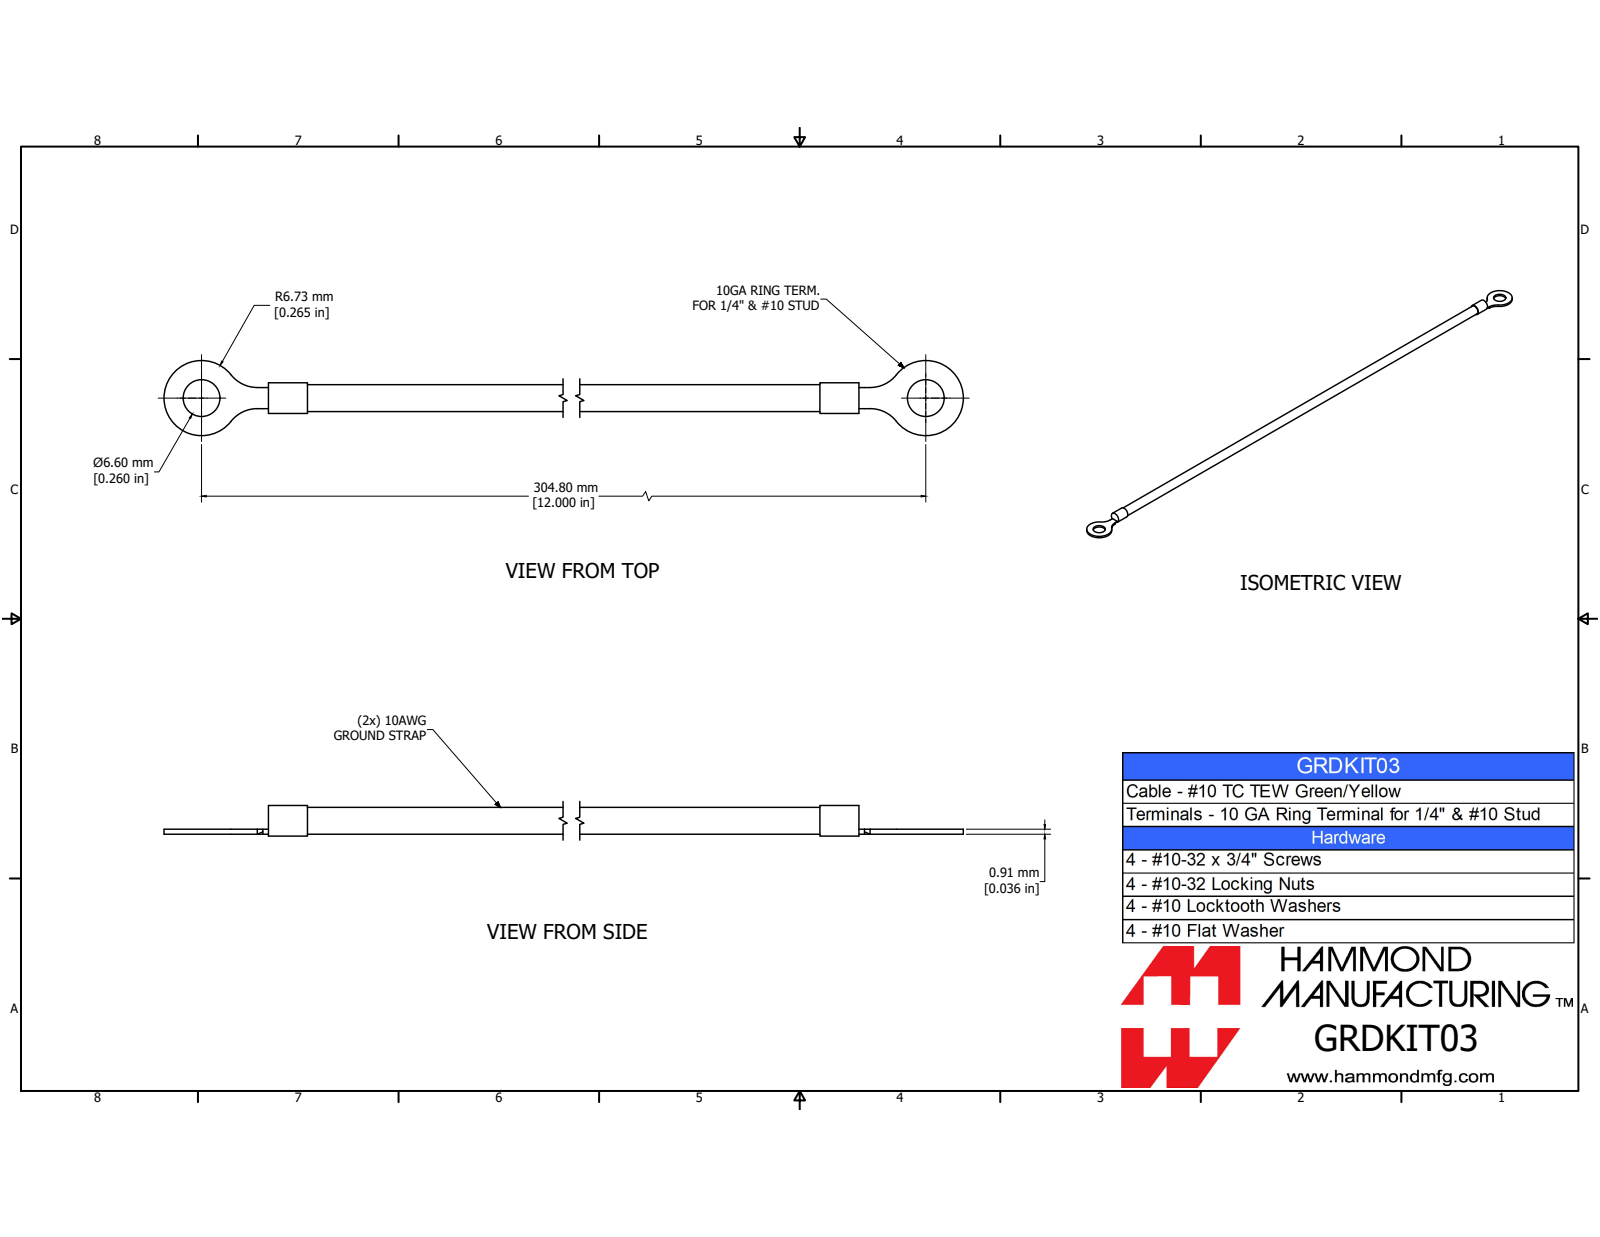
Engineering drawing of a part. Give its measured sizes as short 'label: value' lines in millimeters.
name: GRDKIT03
written by: Autodesk Inventor 2015 (AUTOMOTIVE_DESIGN)
unit: mm
bodies: 1 solid, 27 faces (8 planar, 13 cylindrical, 6 other)
size: 318.26 × 13.46 × 5.5
volume: 5 450 mm³; area: 4 990 mm²
holes: 2× ⌀6.6
bosses: 1× ⌀5.5, 1× ⌀4.83
rounds: 4× R6.02, 2× R6.73
face distances: 0.91, 280.8, 7, 273.8, 266.8
hole spacings: 304.8
